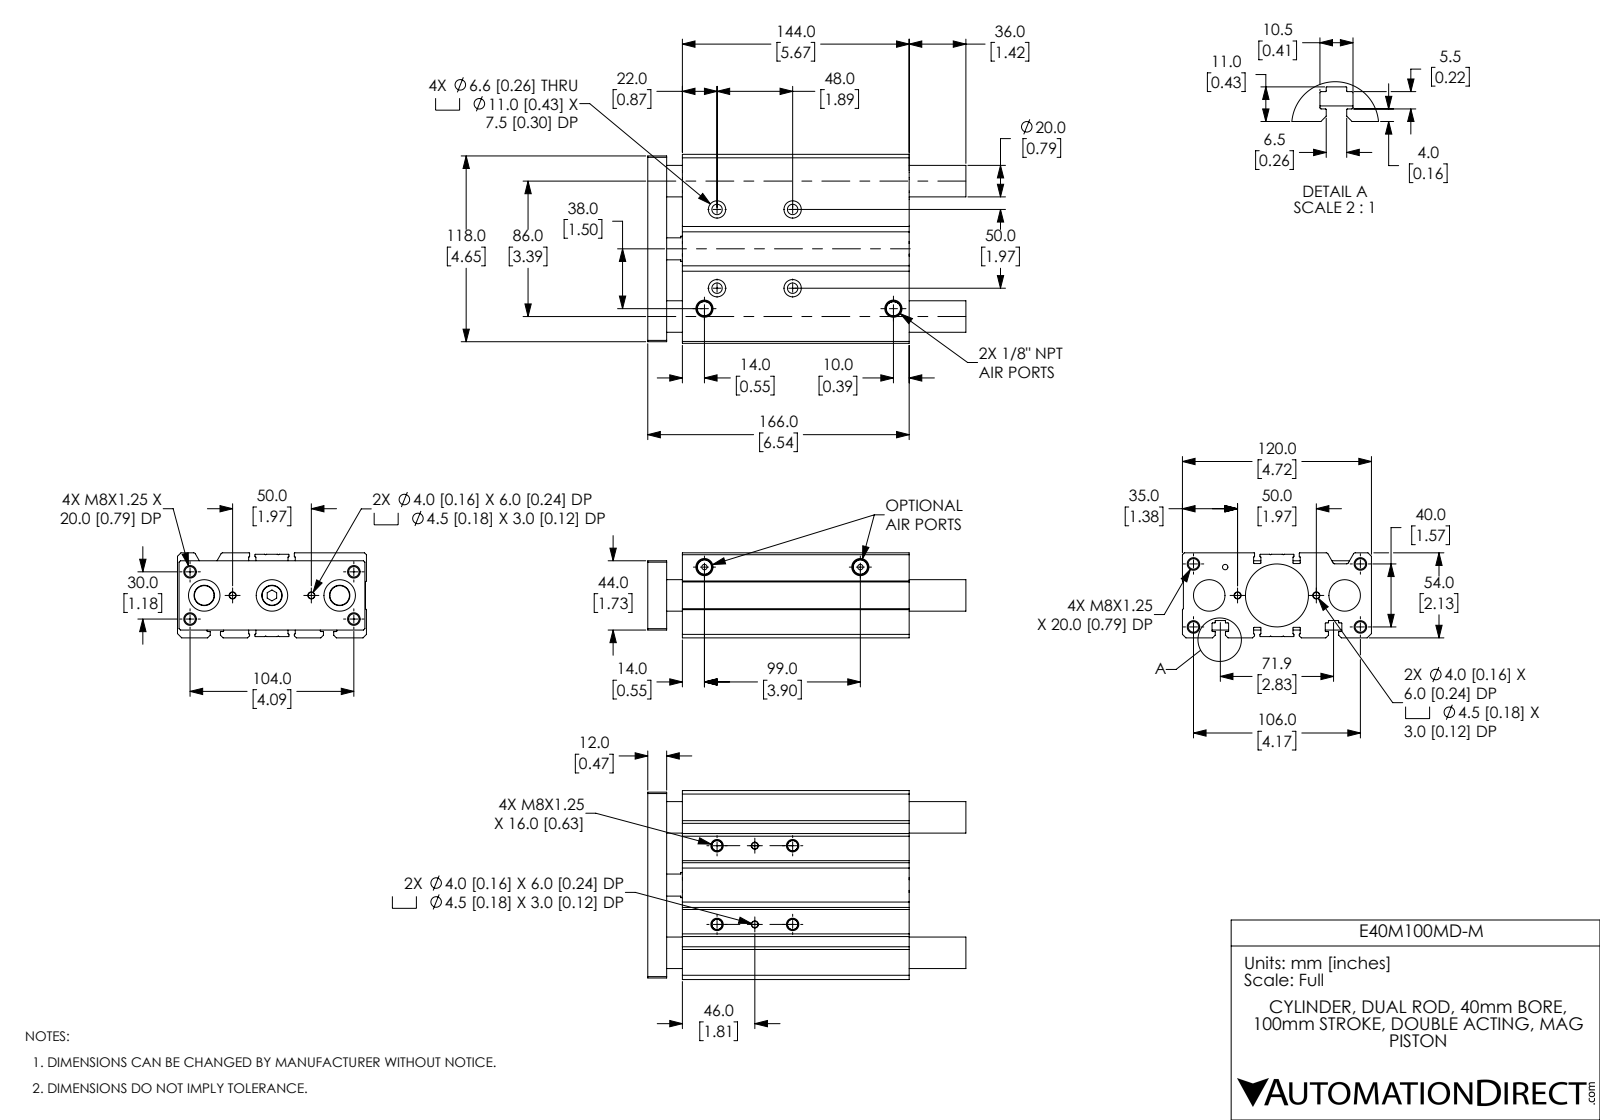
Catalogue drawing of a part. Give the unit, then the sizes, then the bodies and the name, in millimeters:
Units: millimetres
Overall size (bounding box): 202 × 120 × 54
Round holes (diameter × count): ⌀6.65 ×12, ⌀4 ×4, ⌀4.5 ×4, ⌀6.6 ×4, ⌀11 ×4, ⌀3.43 ×3, ⌀10 ×3, ⌀20 ×3, ⌀10.91 ×2, ⌀12.95 ×2, ⌀20 ×1, ⌀40 ×1
Round bosses / shafts (diameter × count): ⌀16 ×1, ⌀12.95 ×1
Partial cylindrical surfaces — rounded edges, fillets, slot ends (radius × count): R0.2 ×32, R0.4 ×28, R1.2 ×4, R0.3 ×2
Main face-to-face distances: 54, 120, 22, 12, 10, 166, 154, 144, 119.4, 0.6
Hole centre spacings: 5.1, 17.49, 22.36, 24, 30.89, 34.41, 35.01, 50
Volume: 832 575 mm³ · Surface area: 178 457 mm²
Bodies: 5 solids, 427 faces (139 planar, 194 cylindrical, 94 other)
Part name (STEP PRODUCT): E40M100MD-M_BODY; E40M100MD-M_ENDPLATE; E40M100MD-M
STEP written by: SolidWorks 2019 (CONFIG_CONTROL_DESIGN)
